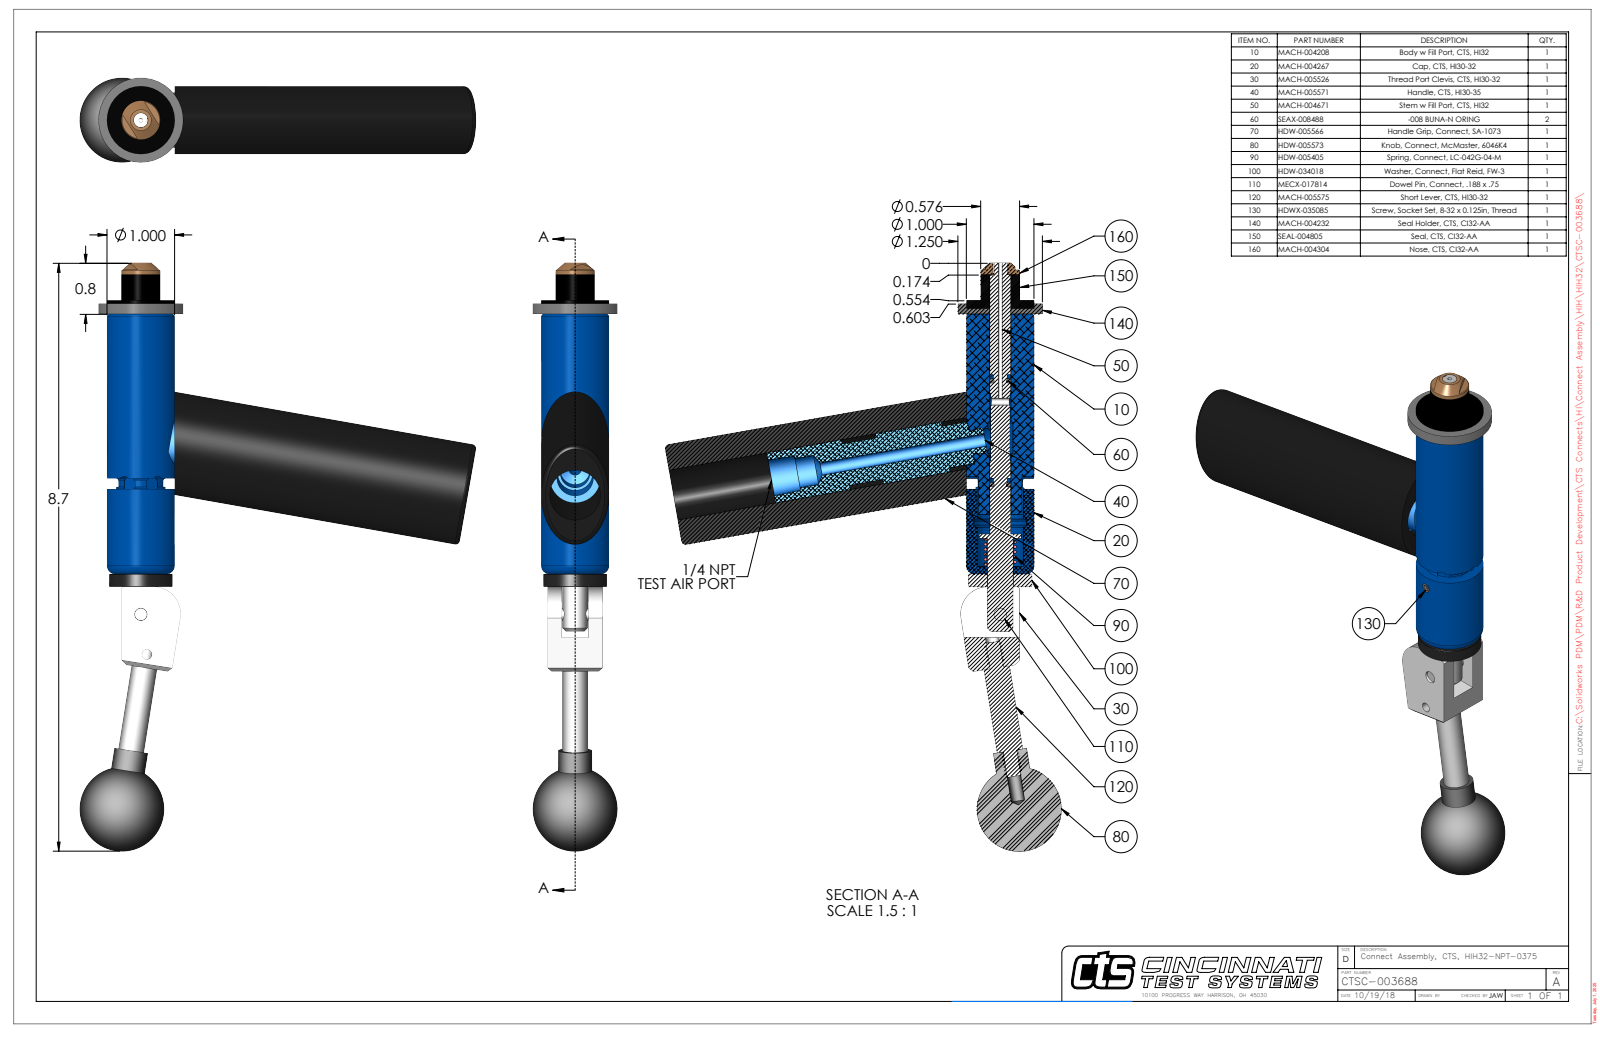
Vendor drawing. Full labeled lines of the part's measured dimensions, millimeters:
Part name (STEP PRODUCT): CTSC-003688
STEP written by: SolidWorks 2023 (AUTOMOTIVE_DESIGN)
Units: millimetres
Bodies: 10 solids, 317 faces (117 planar, 133 cylindrical, 67 other)
Overall size (bounding box): 220.8 × 148.7 × 31.8
Volume: 155 700 mm³ · Surface area: 51 290 mm²
Round holes (diameter × count): ⌀5.1 ×2, ⌀1.6 ×1, ⌀2.8 ×1, ⌀3.5 ×1, ⌀3.8 ×1, ⌀4.7 ×1, ⌀4.8 ×1, ⌀5.4 ×1, ⌀7.9 ×1, ⌀8 ×1, ⌀8 ×1, ⌀9.8 ×1
Round bosses / shafts (diameter × count): ⌀6.4 ×2, ⌀5.1 ×2, ⌀31.8 ×1, ⌀25.4 ×1, ⌀23.8 ×1, ⌀19.1 ×1, ⌀15.7 ×1, ⌀14.7 ×1
Partial cylindrical surfaces — rounded edges, fillets, slot ends (radius × count): R2.4 ×6, R0.7 ×2, R1.5 ×1, R8.3 ×1, R9.5 ×1, R10.2 ×1, R11.9 ×1
Main face-to-face distances: 2.1, 5.3, 15.3, 99.6, 97.5, 20.6, 104.3, 102.3, 4.7, 9.9
Hole centre spacings: 15.2, 42.1, 57.2
